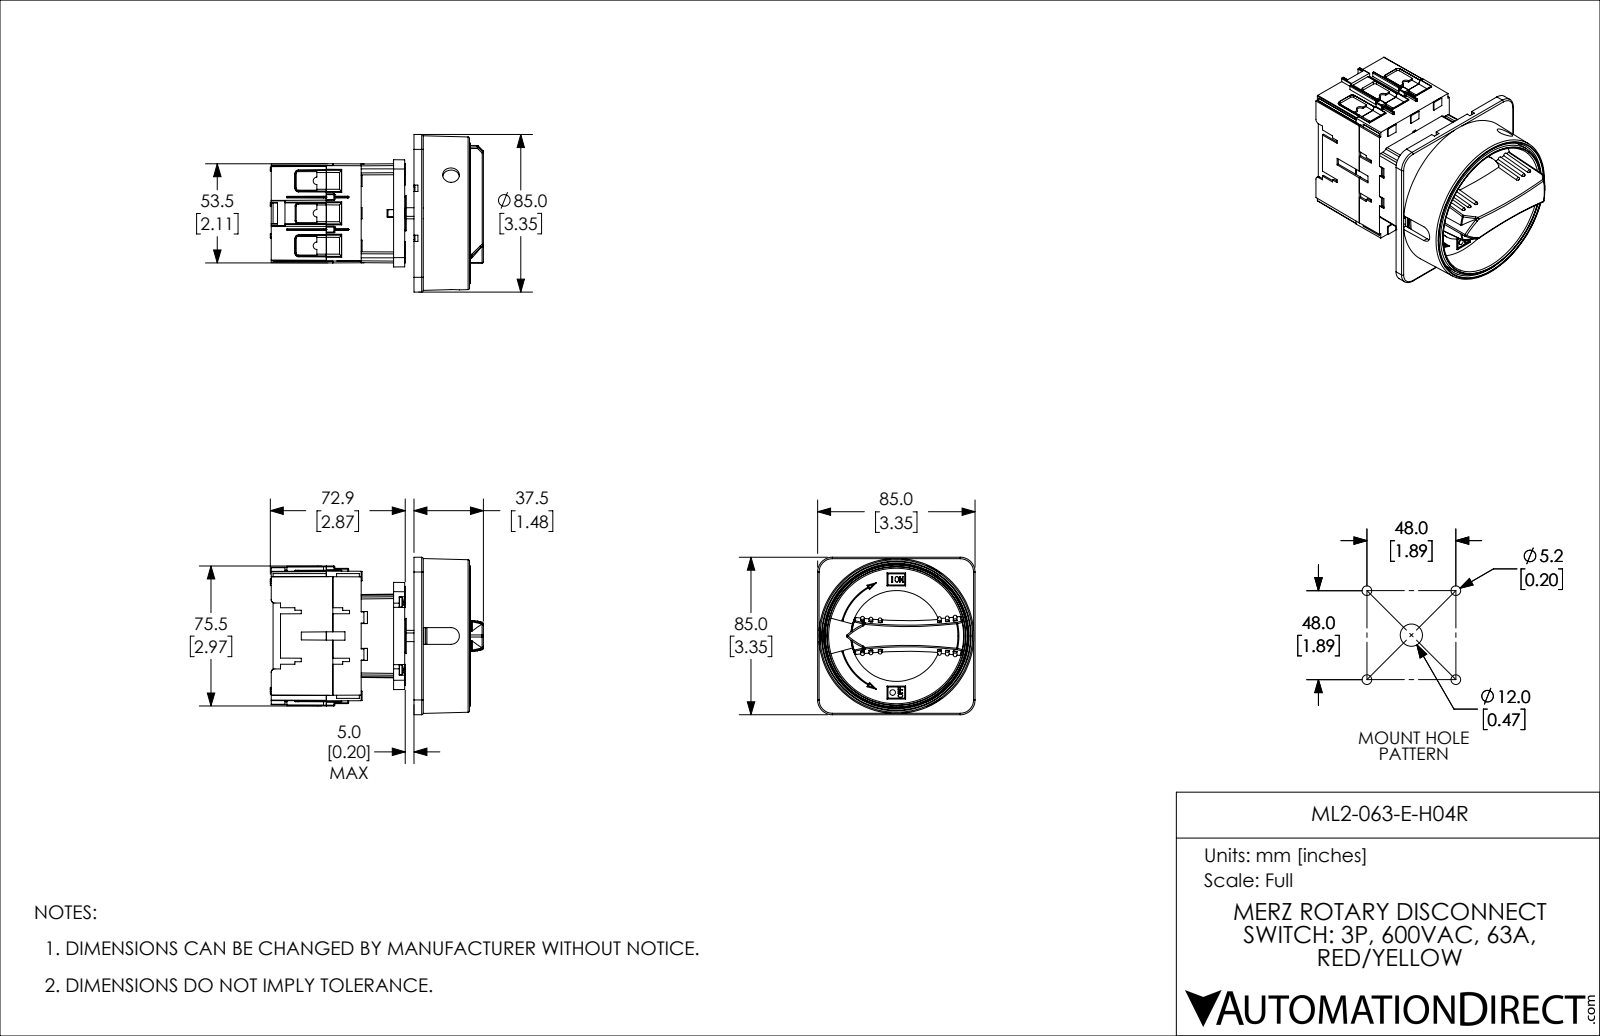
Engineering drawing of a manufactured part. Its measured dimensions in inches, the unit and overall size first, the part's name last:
Units: inches
Overall size (bounding box): 4.53 × 3.346 × 3.346
Round holes (diameter × count): ⌀0.354 ×2, ⌀1.772 ×1, ⌀2.878 ×1
Round bosses / shafts (diameter × count): ⌀0.211 ×6, ⌀0.217 ×4, ⌀0.205 ×4, ⌀3.031 ×1, ⌀3.012 ×1, ⌀1.929 ×1, ⌀1.87 ×1, ⌀0.748 ×1
Partial cylindrical surfaces — rounded edges, fillets, slot ends (radius × count): R0.012 ×43, R0.02 ×29, R0.016 ×28, R0.01 ×14, R0.079 ×11, R0.028 ×8, R0.031 ×4, R0.039 ×4
Main face-to-face distances: 0.138, 0.335, 0.236, 0.079, 0.197, 0.472, 0.039, 0.256, 2.797, 0.276
Volume: 18.56 in³ · Surface area: 158.1 in²
Bodies: 1 solid, 1874 faces (1179 planar, 337 cylindrical, 358 other)
Part name (STEP PRODUCT): ML2-063-E-H04R
STEP written by: SolidWorks 2019 (AUTOMOTIVE_DESIGN)
